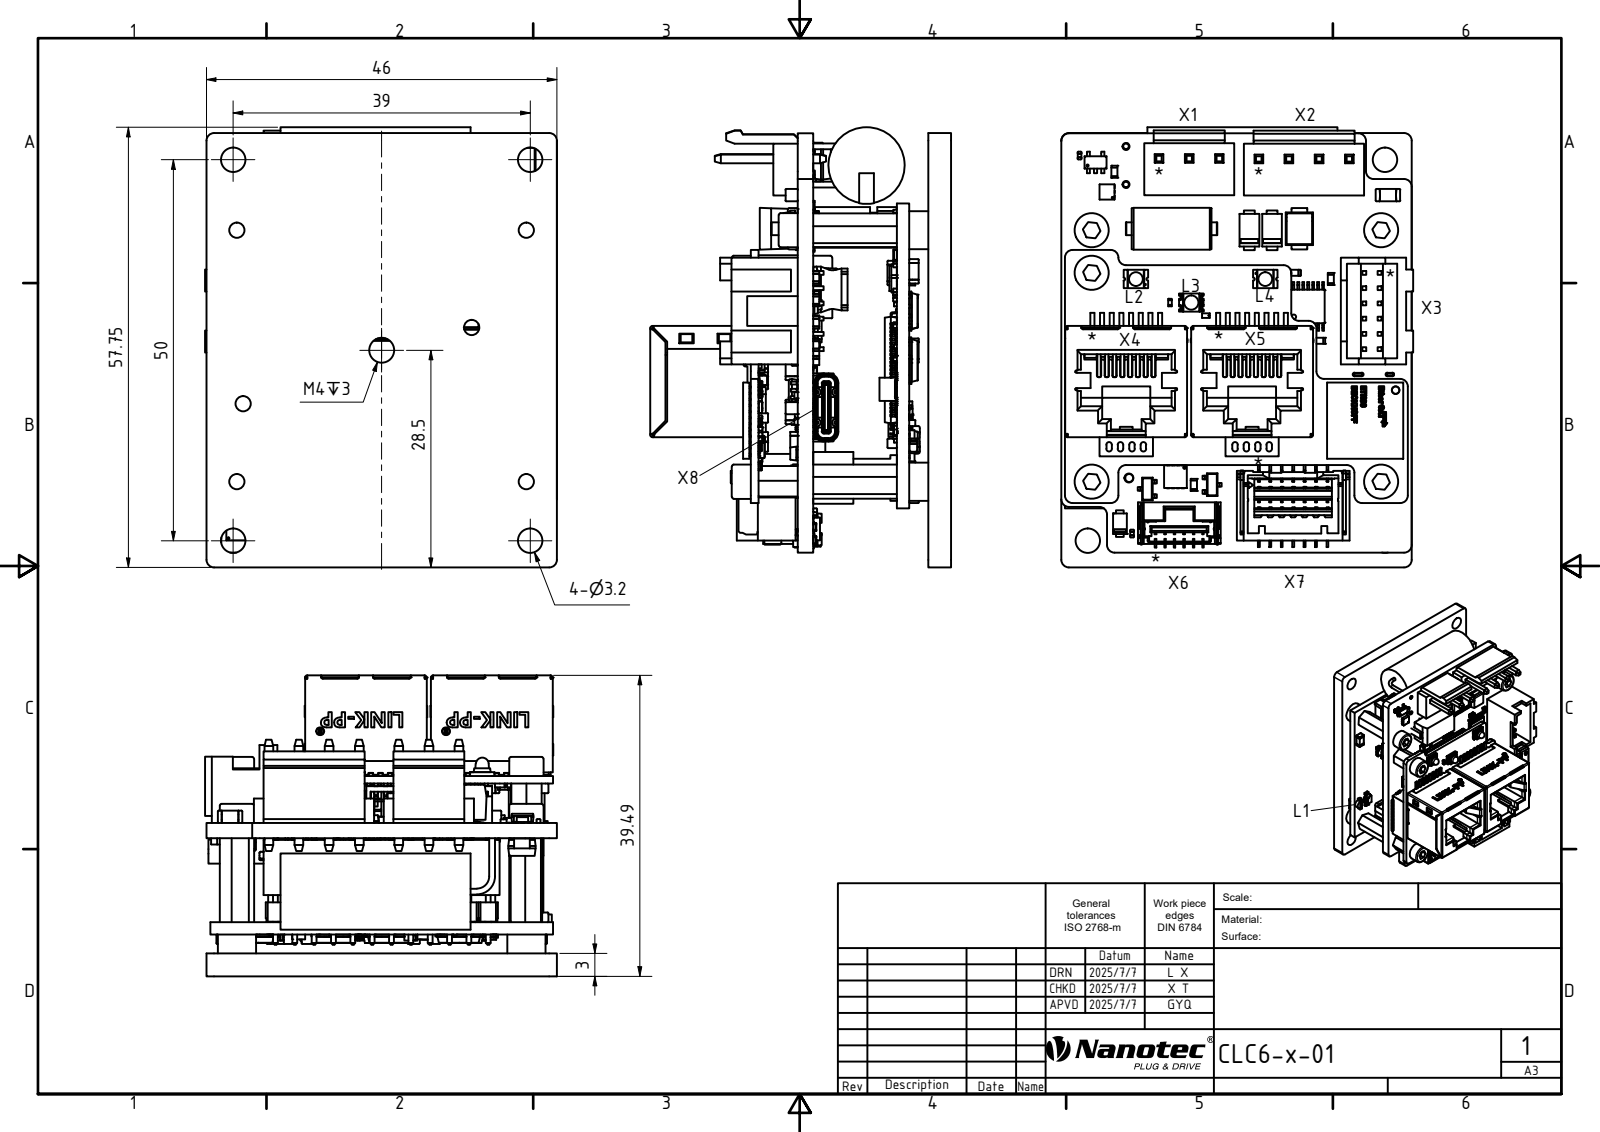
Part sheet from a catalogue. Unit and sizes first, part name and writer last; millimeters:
Units: millimetres
Overall size (bounding box): 57.75 × 46.2 × 39.49
Round holes (diameter × count): ⌀0.91 ×24, ⌀0.7 ×12, ⌀1.7 ×7, ⌀2.01 ×7, ⌀0.3 ×4, ⌀2.51 ×4, ⌀2.6 ×4, ⌀3.2 ×4, ⌀0.25 ×3, ⌀0.6 ×3, ⌀2.7 ×3, ⌀0.5 ×2
Round bosses / shafts (diameter × count): ⌀0.4 ×9, ⌀4.5 ×5, ⌀2.5 ×5, ⌀5 ×4, ⌀1.14 ×4, ⌀1.03 ×4, ⌀1.02 ×4, ⌀0.76 ×4
Partial cylindrical surfaces — rounded edges, fillets, slot ends (radius × count): R0.1 ×1713, R0.12 ×184, R0.2 ×134, R0.15 ×70, R0.21 ×50, R0.35 ×45, R0.5 ×42, R0.3 ×40
Main face-to-face distances: 2.02, 18.11, 17.13, 3, 20.13, 15.11, 2.5, 5.5, 14.63, 12.61
Hole centre spacings: 2.54, 5.08, 5.68, 3.59, 7.62, 8.03, 10.16, 10.47
Bodies: 0 solids, 38156 faces (26793 planar, 7185 cylindrical, 4178 other)
Part name (STEP PRODUCT): CLC6-x-01
STEP written by: Autodesk Inventor 2024 (AUTOMOTIVE_DESIGN)
